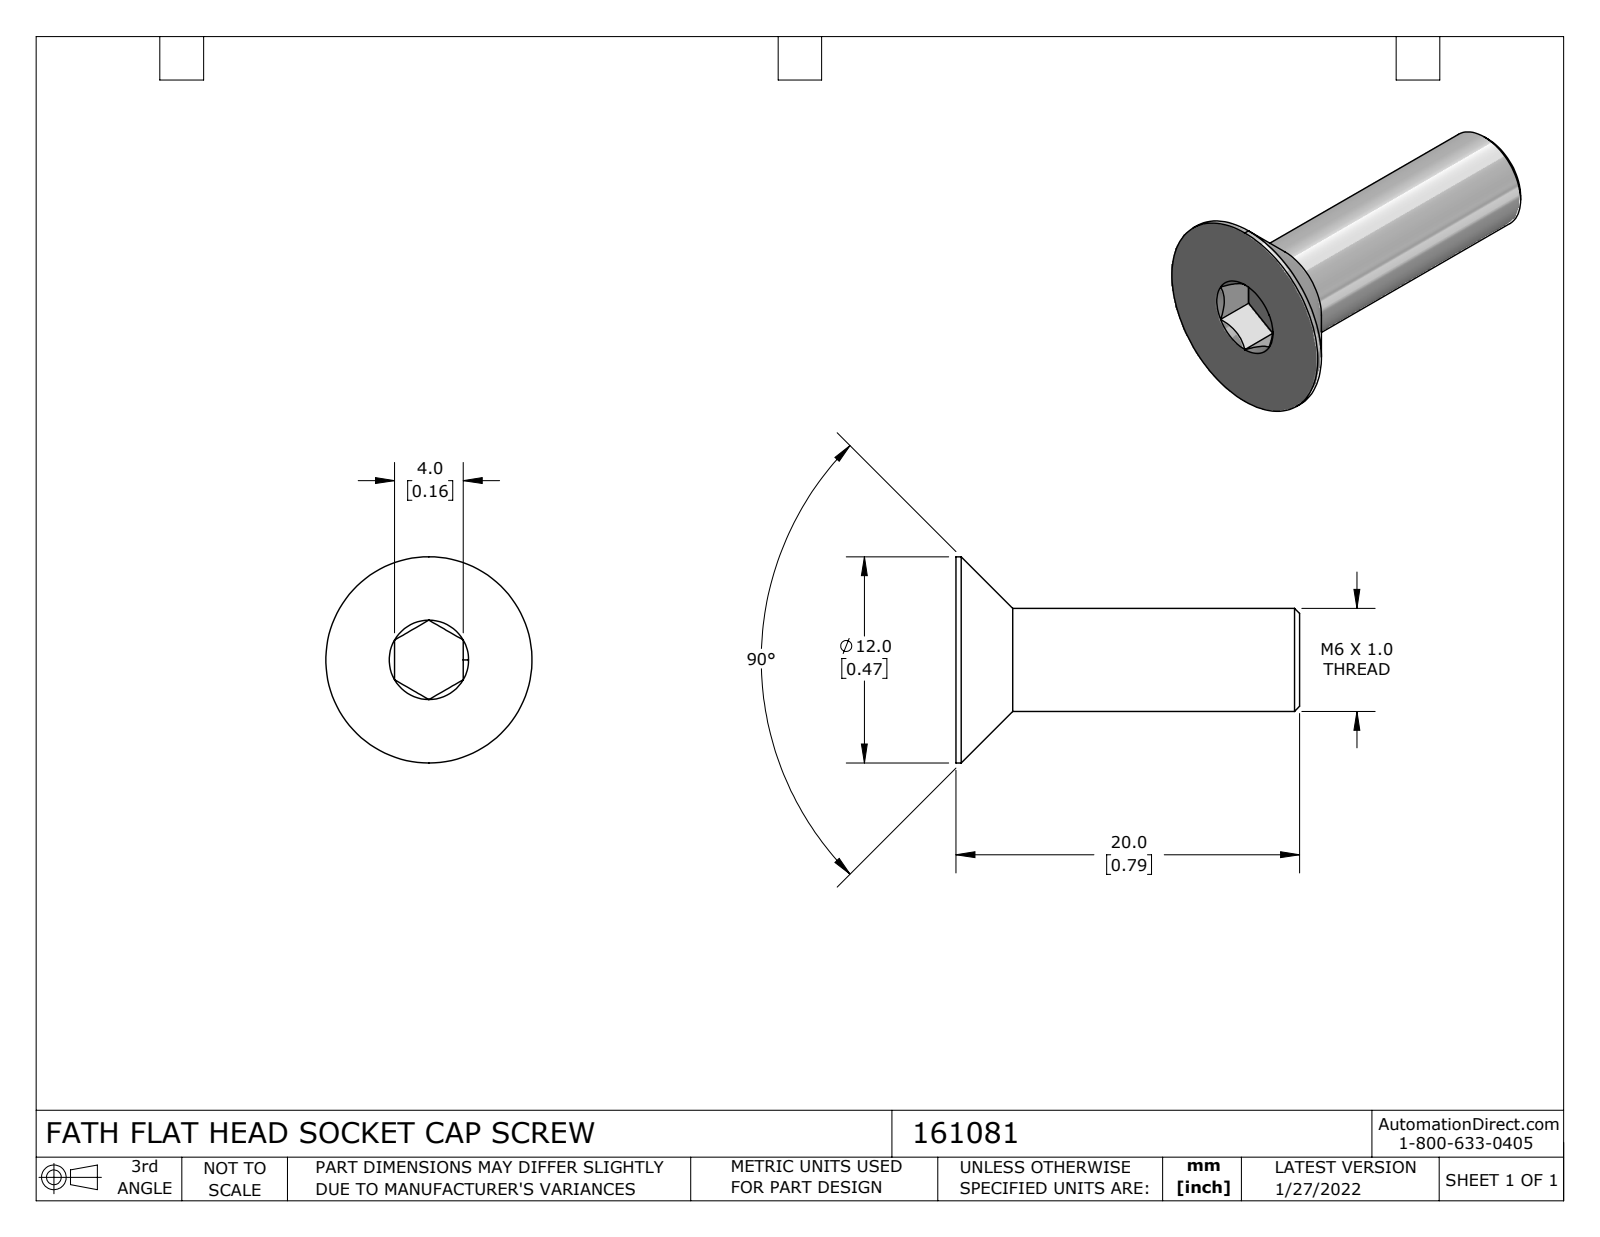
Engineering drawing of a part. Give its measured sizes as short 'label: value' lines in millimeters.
name: 161081
written by: SolidWorks 2021 (CONFIG_CONTROL_DESIGN)
unit: mm
bodies: 1 solid, 24 faces (9 planar, 4 cylindrical, 11 other)
size: 20 × 12 × 12
volume: 671 mm³; area: 614 mm²
bosses: 1× ⌀12, 1× ⌀6
face distances: 20, 4, 17.69, 2.31
